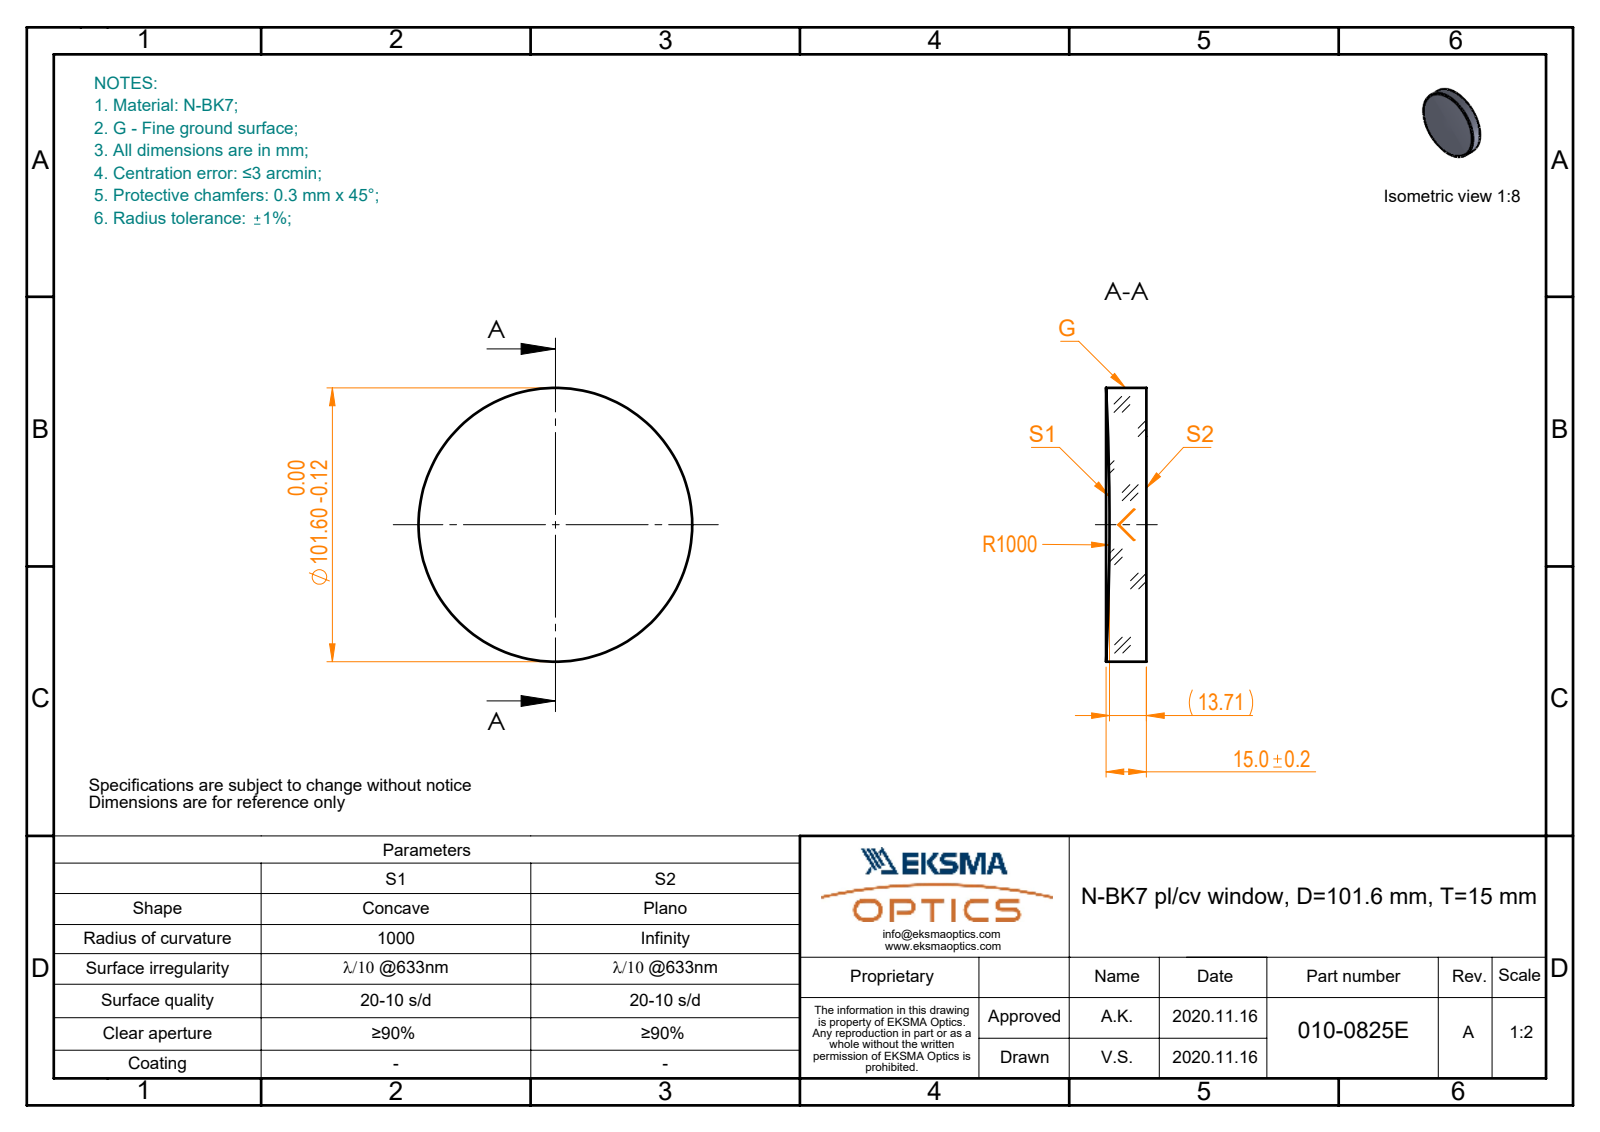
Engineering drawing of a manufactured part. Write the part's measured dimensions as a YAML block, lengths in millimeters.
part_name: "010-0825E_N-BK7_PCV_window"
step_written_by: "SolidWorks 2019 (CONFIG_CONTROL_DESIGN)"
units: millimeters
bodies: {solids: 1, faces: 5, planar: 1, cylindrical: 2, other: 2}
overall_size: [101.6, 101.6, 15]
volume: 116375
surface_area: 21008
round_bosses_or_shafts:
  - {diameter: 101.6, count: 1}
